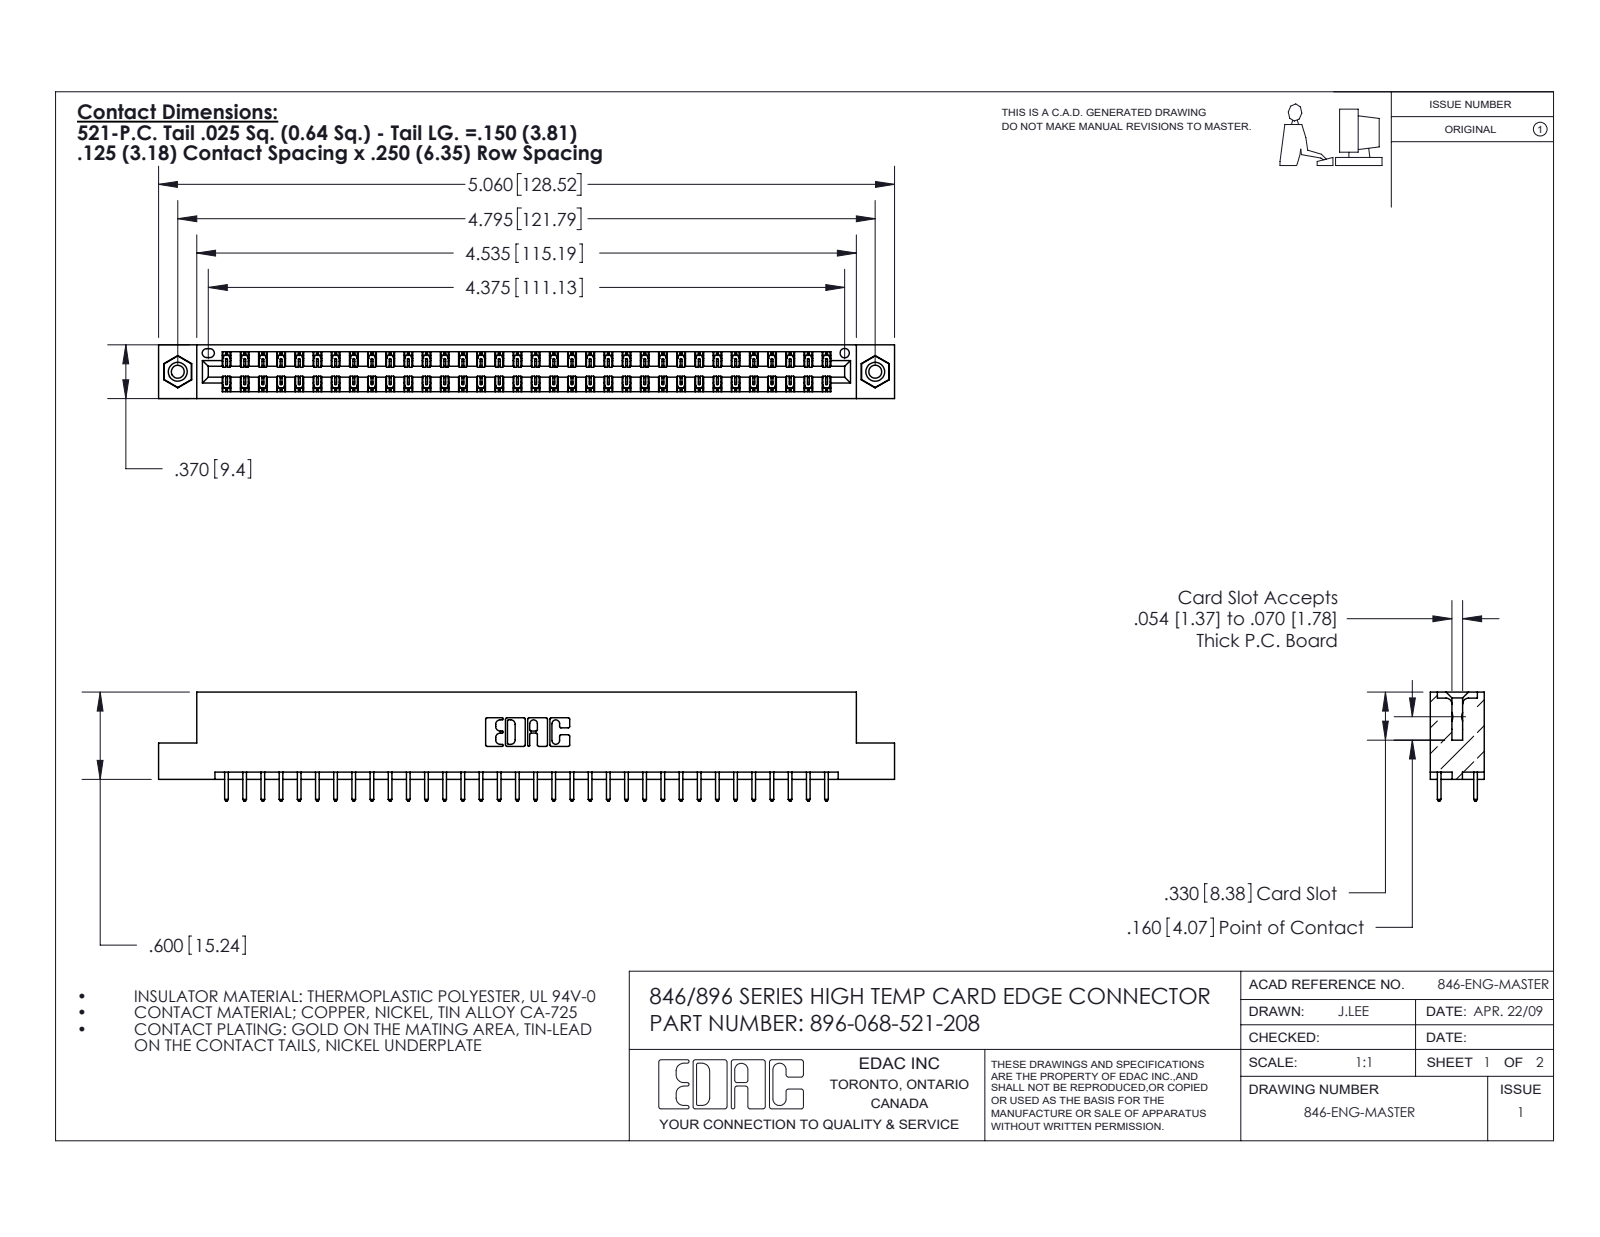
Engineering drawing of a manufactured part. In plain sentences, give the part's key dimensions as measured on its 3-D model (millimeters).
The part is named "346 Part_Flush Mounting Lugs - 0.156 Dia-TI; 345-250-001_345-250-003-102; 396-068-521-208; 345-292-001_345-293-121". Its 3-D file was written by "SolidWorks 2016 (CONFIG_CONTROL_DESIGN)". It is 71 solids with 3718 faces: 2488 planar, 1214 cylindrical and 16 other. Overall it measures 128.5 by 19.1 by 9.4 millimeters. Its volume is 12 400 cubic millimeters and its surface area 16 800 square millimeters. Round holes: 2 of diameter 2.3, 2 of diameter 3.2, 2 of diameter 4, 1 of diameter 1.6. Round bosses or shafts: 2 of diameter 3.9. Partial cylindrical surfaces (rounded edges, fillets, slot ends): 102 of radius 0.2, 68 of radius 0.3, 22 of radius 0.3, 6 of radius 0.2, 6 of radius 0.8, 3 of radius 0.7, 2 of radius 0.4, 2 of radius 0.6. The main face-to-face distances are 1.2, 8.2, 6.4, 9.4, 1.8, 7.6, 0.6, 7, 3.8, 5.6. The hole center spacings are 6.2, 116.5, 121.8.
